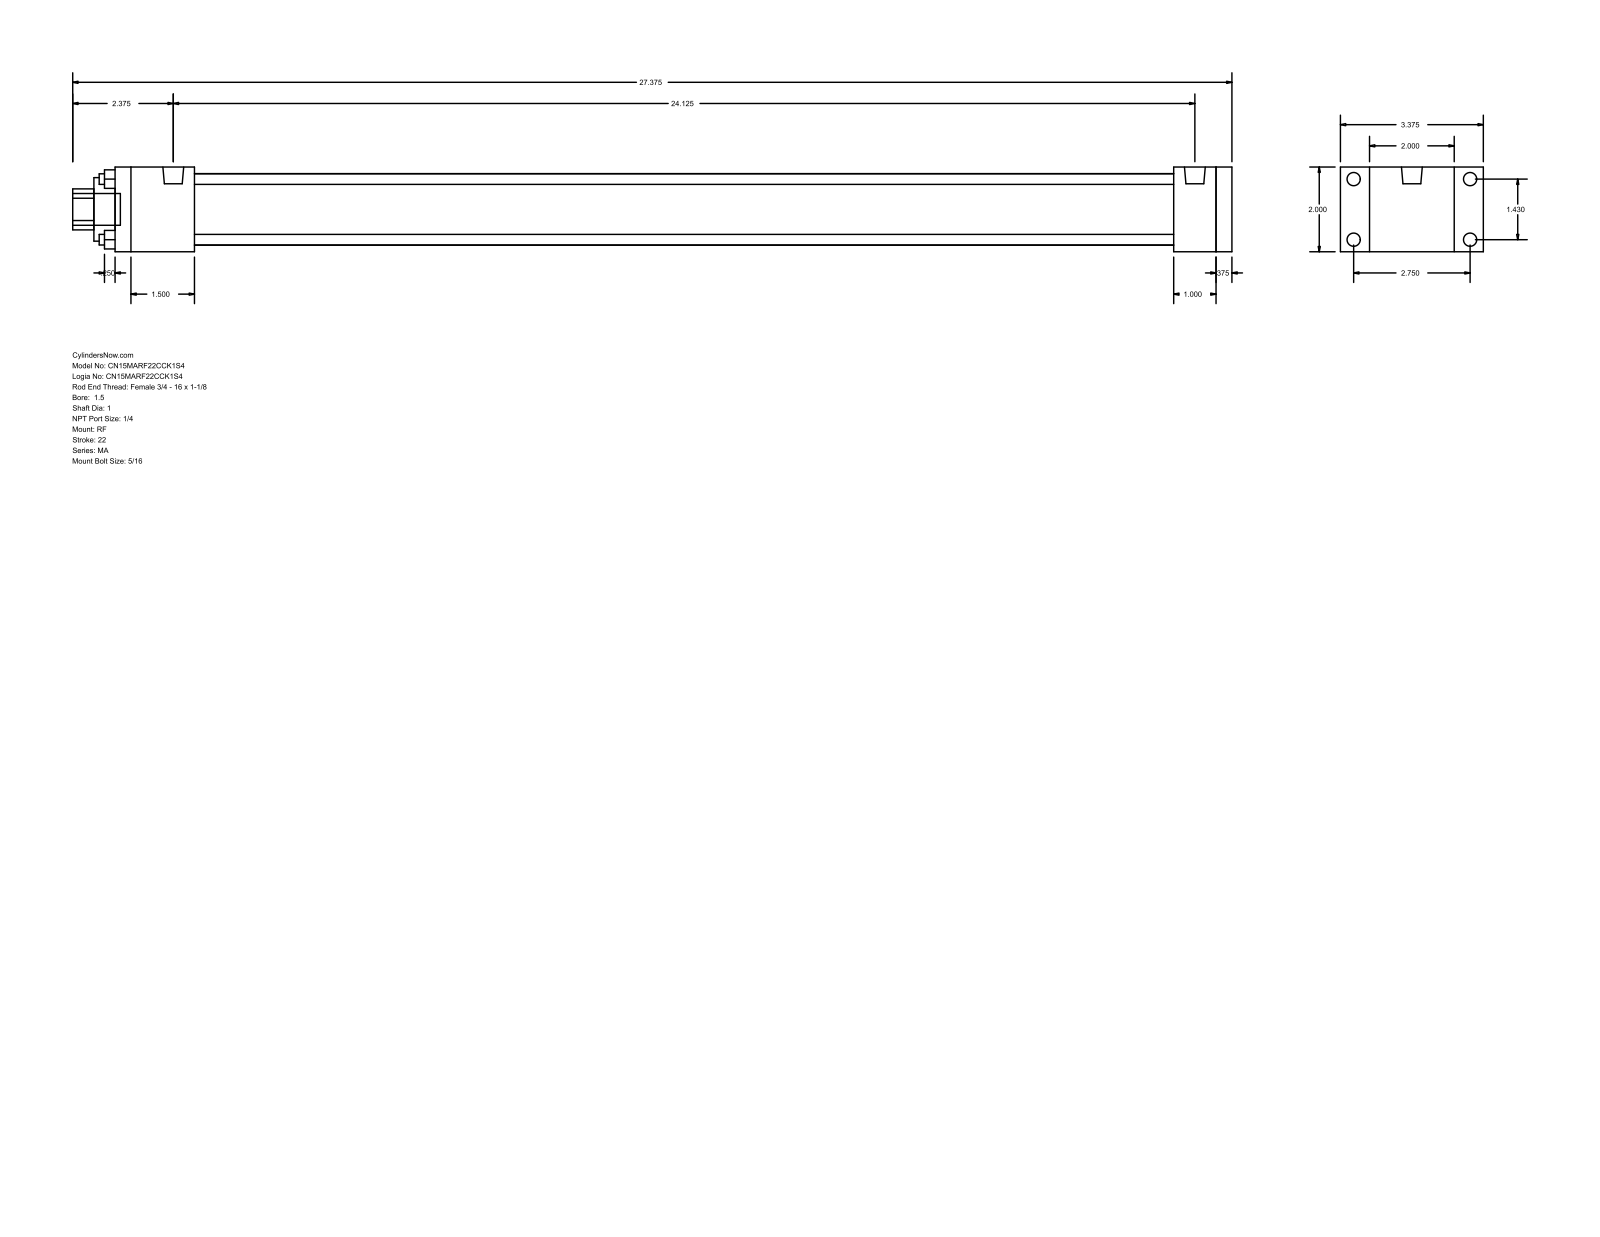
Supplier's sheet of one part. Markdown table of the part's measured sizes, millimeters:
| quantity | value |
| --- | --- |
| part name | MA_RF__0150_1 |
| STEP written by | GSSL Pune (CONFIG_CONTROL_DESIGN) |
| units | millimeters |
| bodies | 0 solids, 92 faces (64 planar, 28 cylindrical, 0 other) |
| overall size | 695.33 × 85.72 × 50.8 |
| round holes (diameter × count) | 6.35 × 4, 25.4 × 1, 38.1 × 1, 42.93 × 1 |
| round bosses / shafts (diameter × count) | 7.94 × 8, 12.49 × 2, 19.05 × 1 |
| partial cylindrical surfaces (radius × count) | 12.29 × 1 |
| main face-to-face distances | 50.8, 9.53, 660.4, 25.4, 669.93, 635, 34.93, 47.63, 587.37, 612.77 |
| hole center spacings | 25.68, 36.32, 51.36 |
